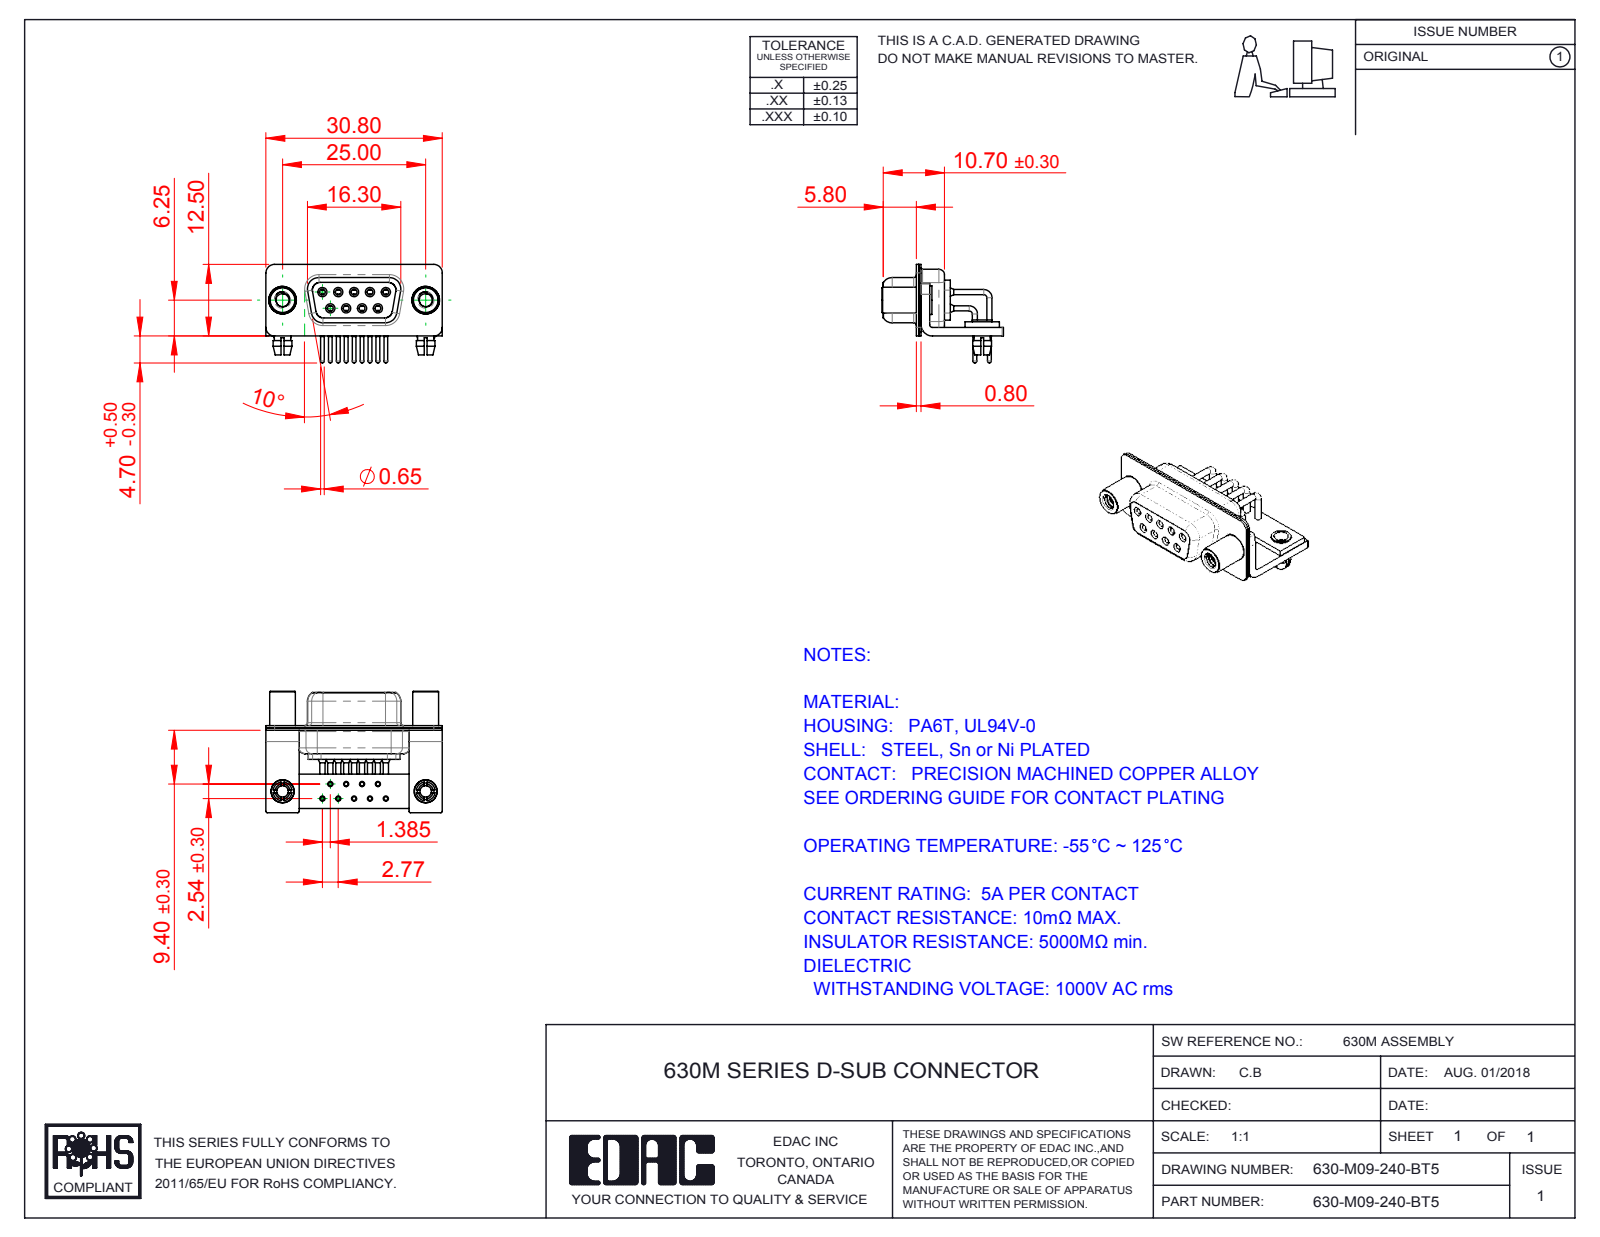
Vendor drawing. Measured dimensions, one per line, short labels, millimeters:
name: 630M Housing_09 Contacts; 630M Shell Rear_09 Contacts; 630-M09-240-BT5; 630M Shell Front_09 Contacts (+6 more)
written by: SolidWorks 2016 (CONFIG_CONTROL_DESIGN)
unit: mm
bodies: 19 solids, 966 faces (278 planar, 458 cylindrical, 230 other)
size: 30.8 × 21.2 × 17.2
volume: 2 364 mm³; area: 6 238 mm²
holes: 11× ⌀2, 9× ⌀0.9, 9× ⌀1, 9× ⌀1.1, 9× ⌀1.7, 9× ⌀1.8, 2× ⌀2.26, 2× ⌀2.5, 2× ⌀3.2, 2× ⌀4, 2× ⌀4.8
bosses: 9× ⌀1.6, 9× ⌀1.5, 9× ⌀0.9, 9× ⌀0.65, 2× ⌀5, 2× ⌀4.9, 2× ⌀4.5, 2× ⌀4
rounds: 16× R0.25, 16× R1.5, 13× R2, 8× R1.35, 8× R1.6, 5× R0.5, 4× R0.6, 4× R0.65
face distances: 0.4, 1.5, 0.8, 2.3, 1.9, 1, 9.35, 1.45, 8.5, 8.95
hole spacings: 2.77, 5.54, 3.16, 4.87, 8.31, 2.89, 2.9, 5.03
